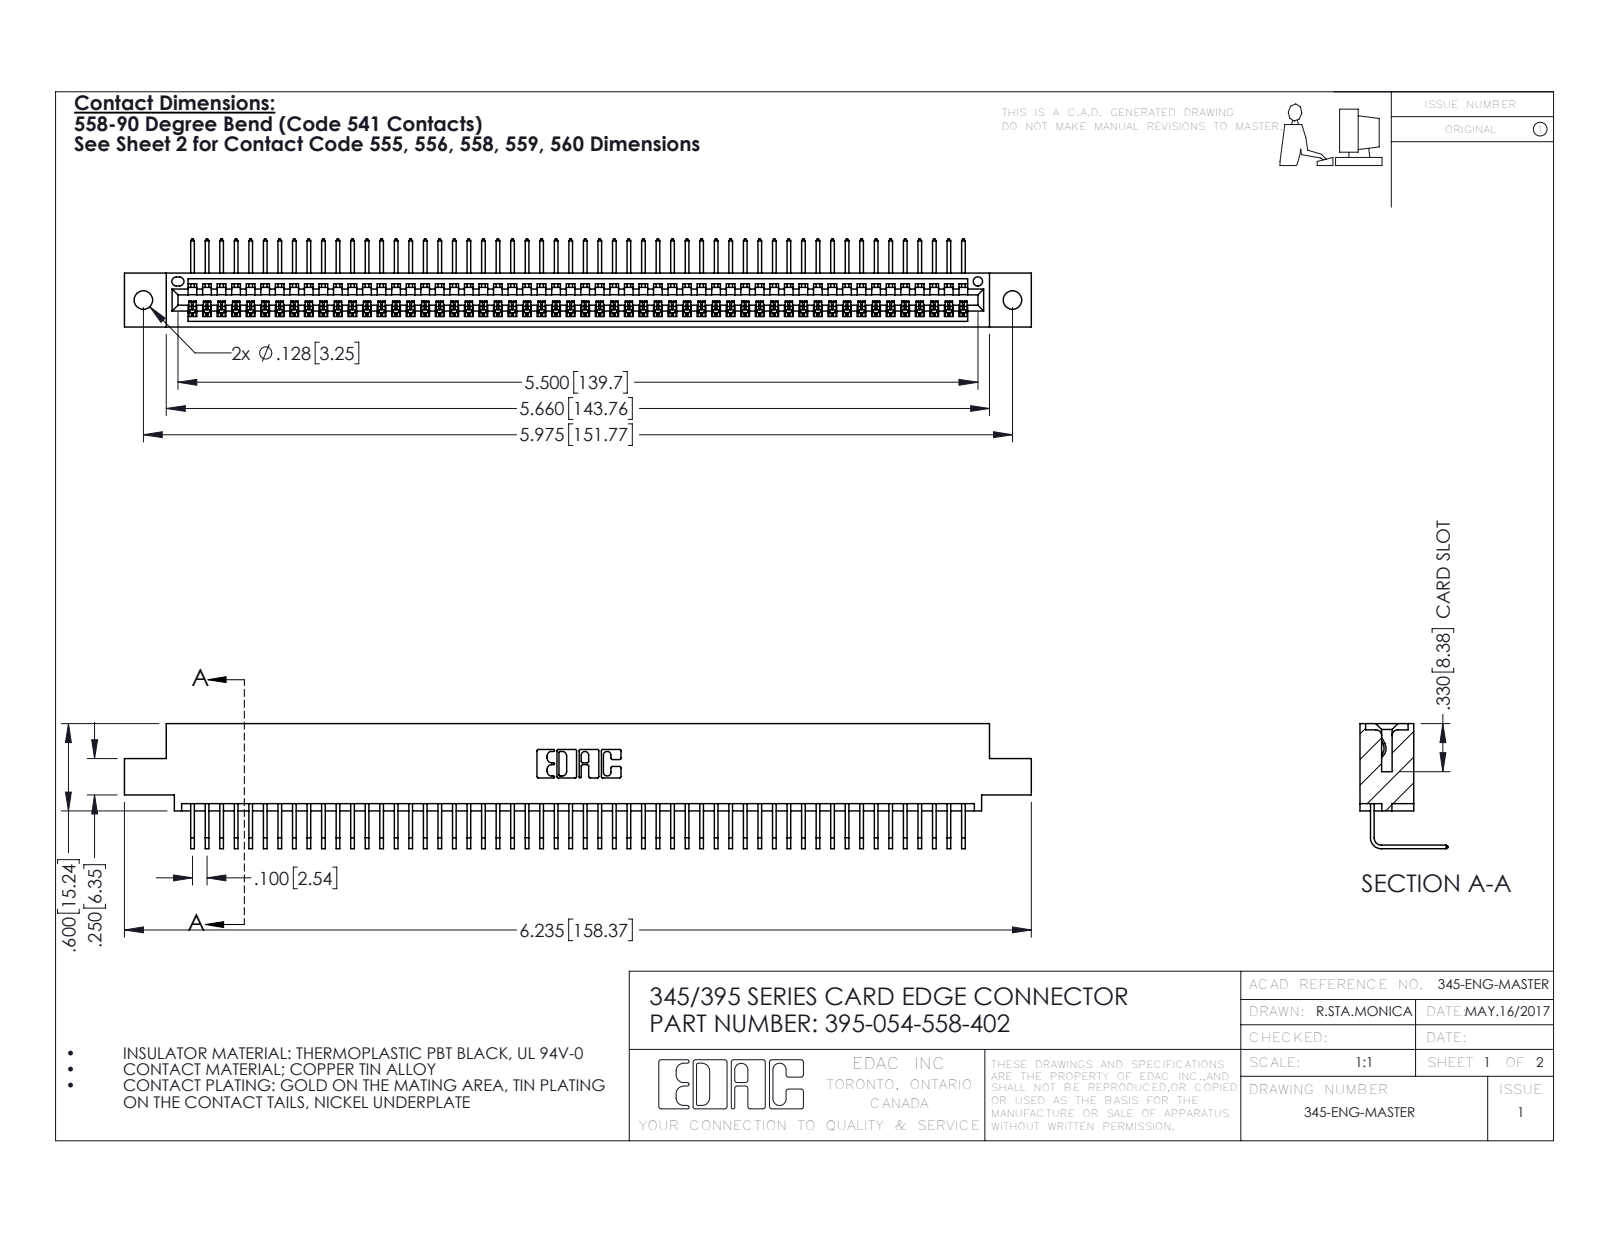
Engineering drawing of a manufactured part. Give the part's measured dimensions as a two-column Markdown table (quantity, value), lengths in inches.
| quantity | value |
| --- | --- |
| part name | 345-292-001_558 Tail - 2; 345 Part_0.110 Offset - 0.128 Dia; 395-054-558-402 |
| STEP written by | SolidWorks 2016 (CONFIG_CONTROL_DESIGN) |
| units | inches |
| bodies | 55 solids, 3370 faces (2352 planar, 1018 cylindrical, 0 other) |
| overall size | 6.235 × 0.859 × 0.605 |
| volume | 0.928 in³ |
| surface area | 32.93 in² |
| round holes (diameter × count) | 0.128 × 2, 0.064 × 1 |
| partial cylindrical surfaces (radius × count) | 0.006 × 108, 0.01 × 22, 0.007 × 6, 0.031 × 6, 0.026 × 3, 0.031 × 2, 0.04 × 2, 0.014 × 1 |
| main face-to-face distances | 0.072, 0.298, 0.37, 0.2, 0.098, 0.272, 0.025, 0.225, 0.149, 0.072 |
| hole center spacings | 0.27, 5.739, 5.975 |
